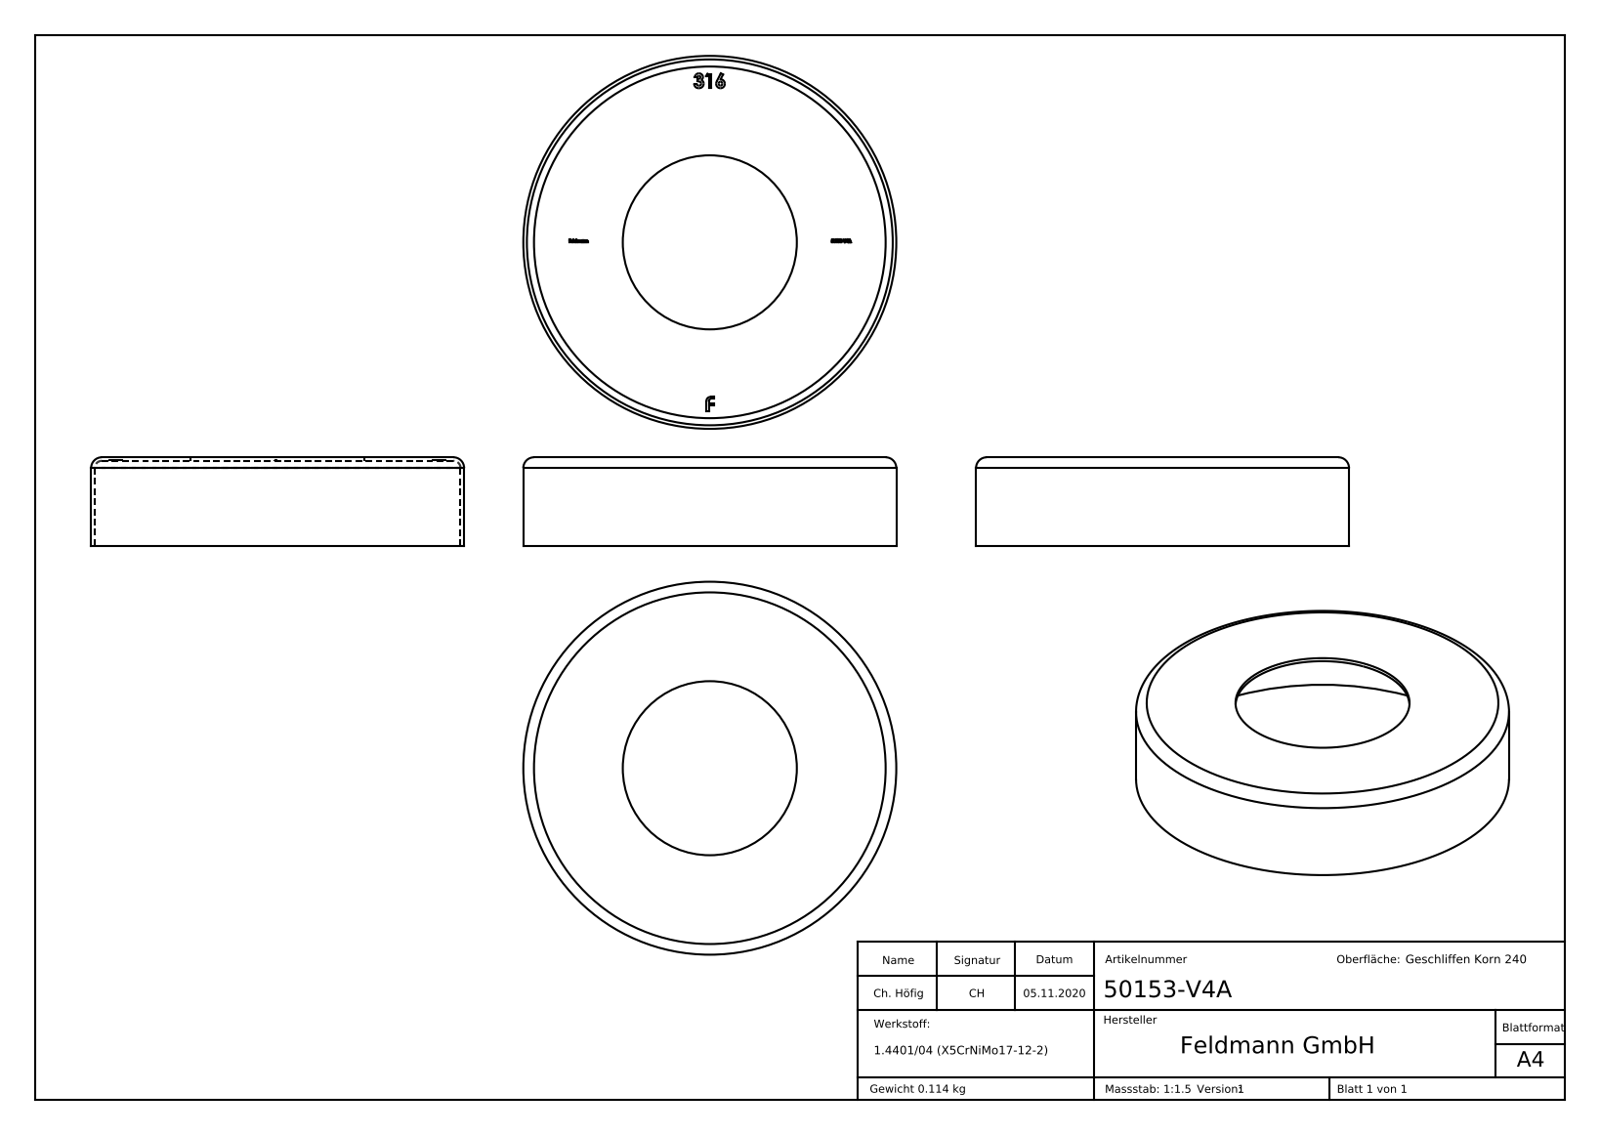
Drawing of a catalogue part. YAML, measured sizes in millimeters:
part_name: "50153-V4A"
step_written_by: "SolidWorks 2018 (CONFIG_CONTROL_DESIGN)"
units: millimeters
bodies: {solids: 1, faces: 283, planar: 163, cylindrical: 6, other: 114}
overall_size: [105, 105, 25]
volume: 14259
surface_area: 29016
round_holes:
  - {diameter: 49, count: 1}
  - {diameter: 103, count: 1}
round_bosses_or_shafts:
  - {diameter: 105, count: 1}
face_to_face_distances: [1, 24, 25, 24.1, 0.9, 0.71, 0.73, 1.44, 0.75, 46.02]
